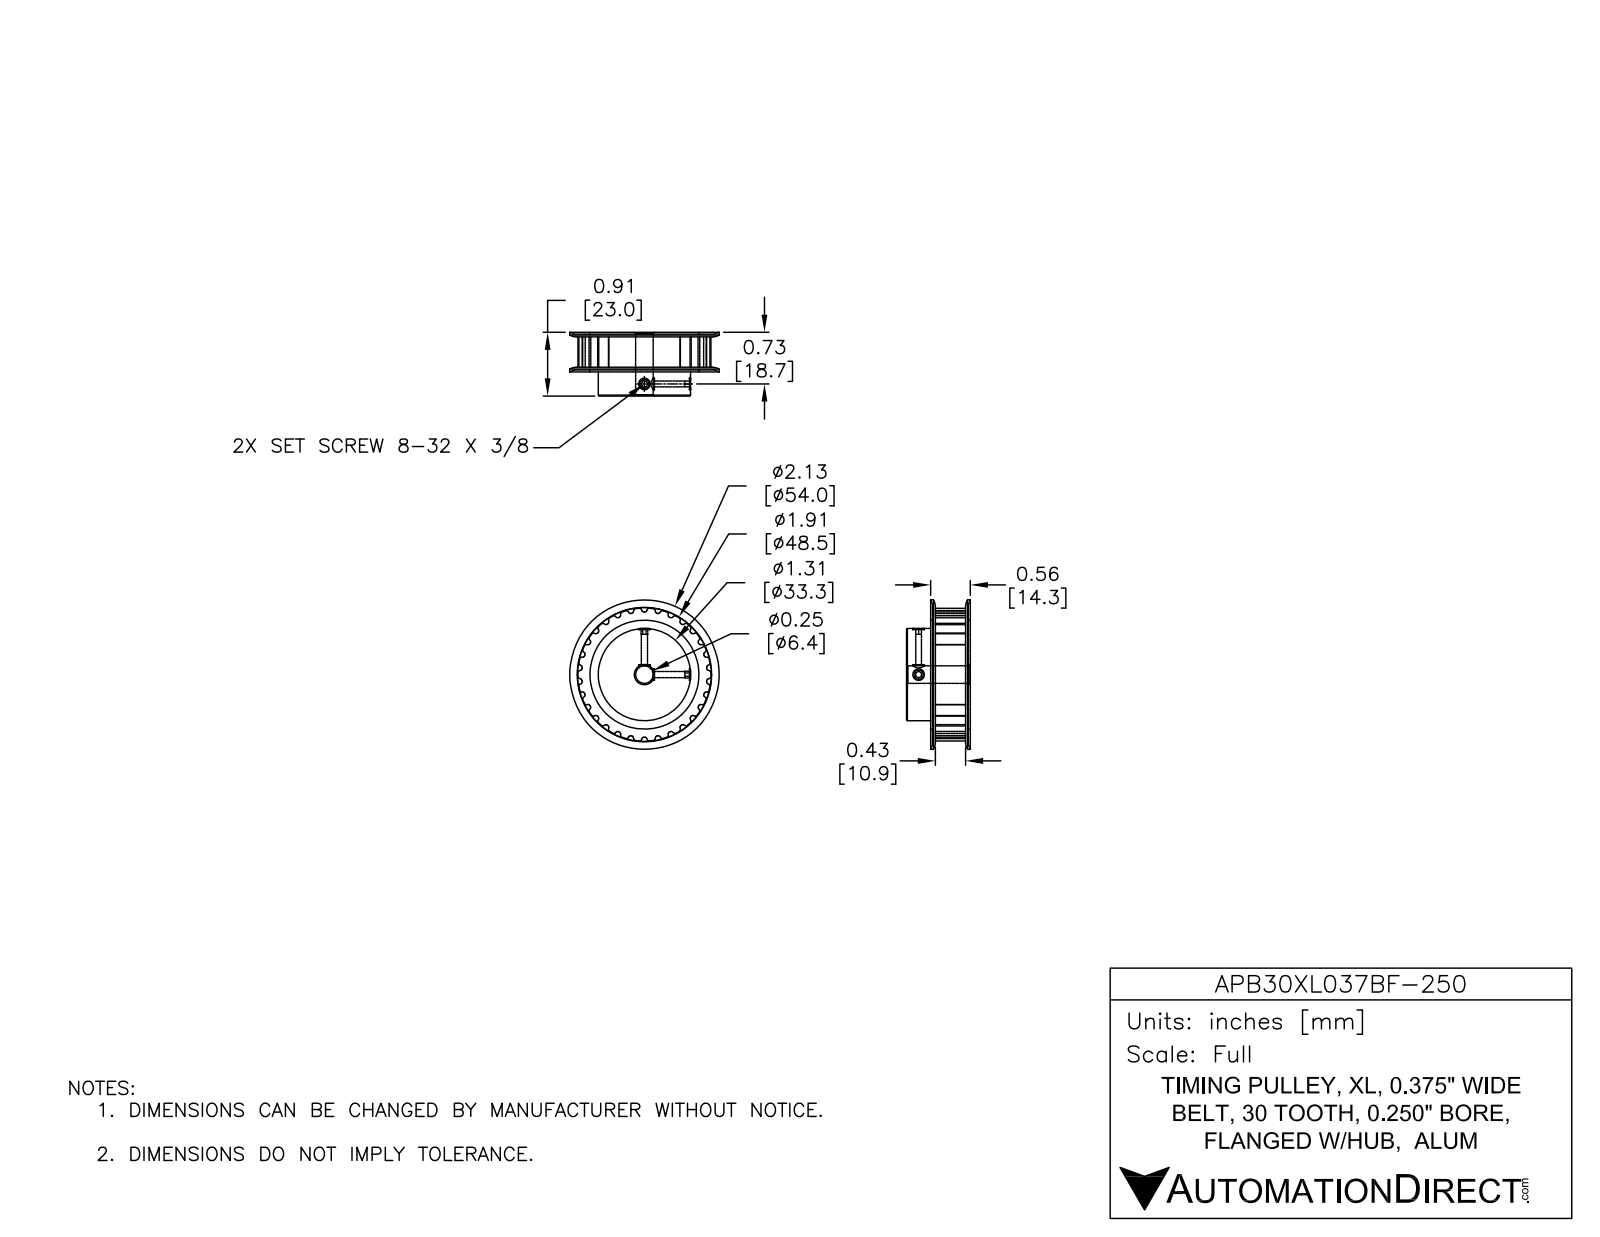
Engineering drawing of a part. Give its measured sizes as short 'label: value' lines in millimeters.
name: APB30XL037BF-250
written by: SolidWorks 2014 (AUTOMOTIVE_DESIGN)
unit: mm
bodies: 1 solid, 297 faces (96 planar, 179 cylindrical, 22 other)
size: 53.98 × 53.98 × 23.01
volume: 30 945 mm³; area: 9 735 mm²
holes: 2× ⌀2.23, 1× ⌀6.35
bosses: 1× ⌀33.35
rounds: 120× R0.38, 1× R22.61
face distances: 12.57, 0.83, 13.4, 23.01, 22.18, 9.61, 17.96, 48, 1.65, 0.82
